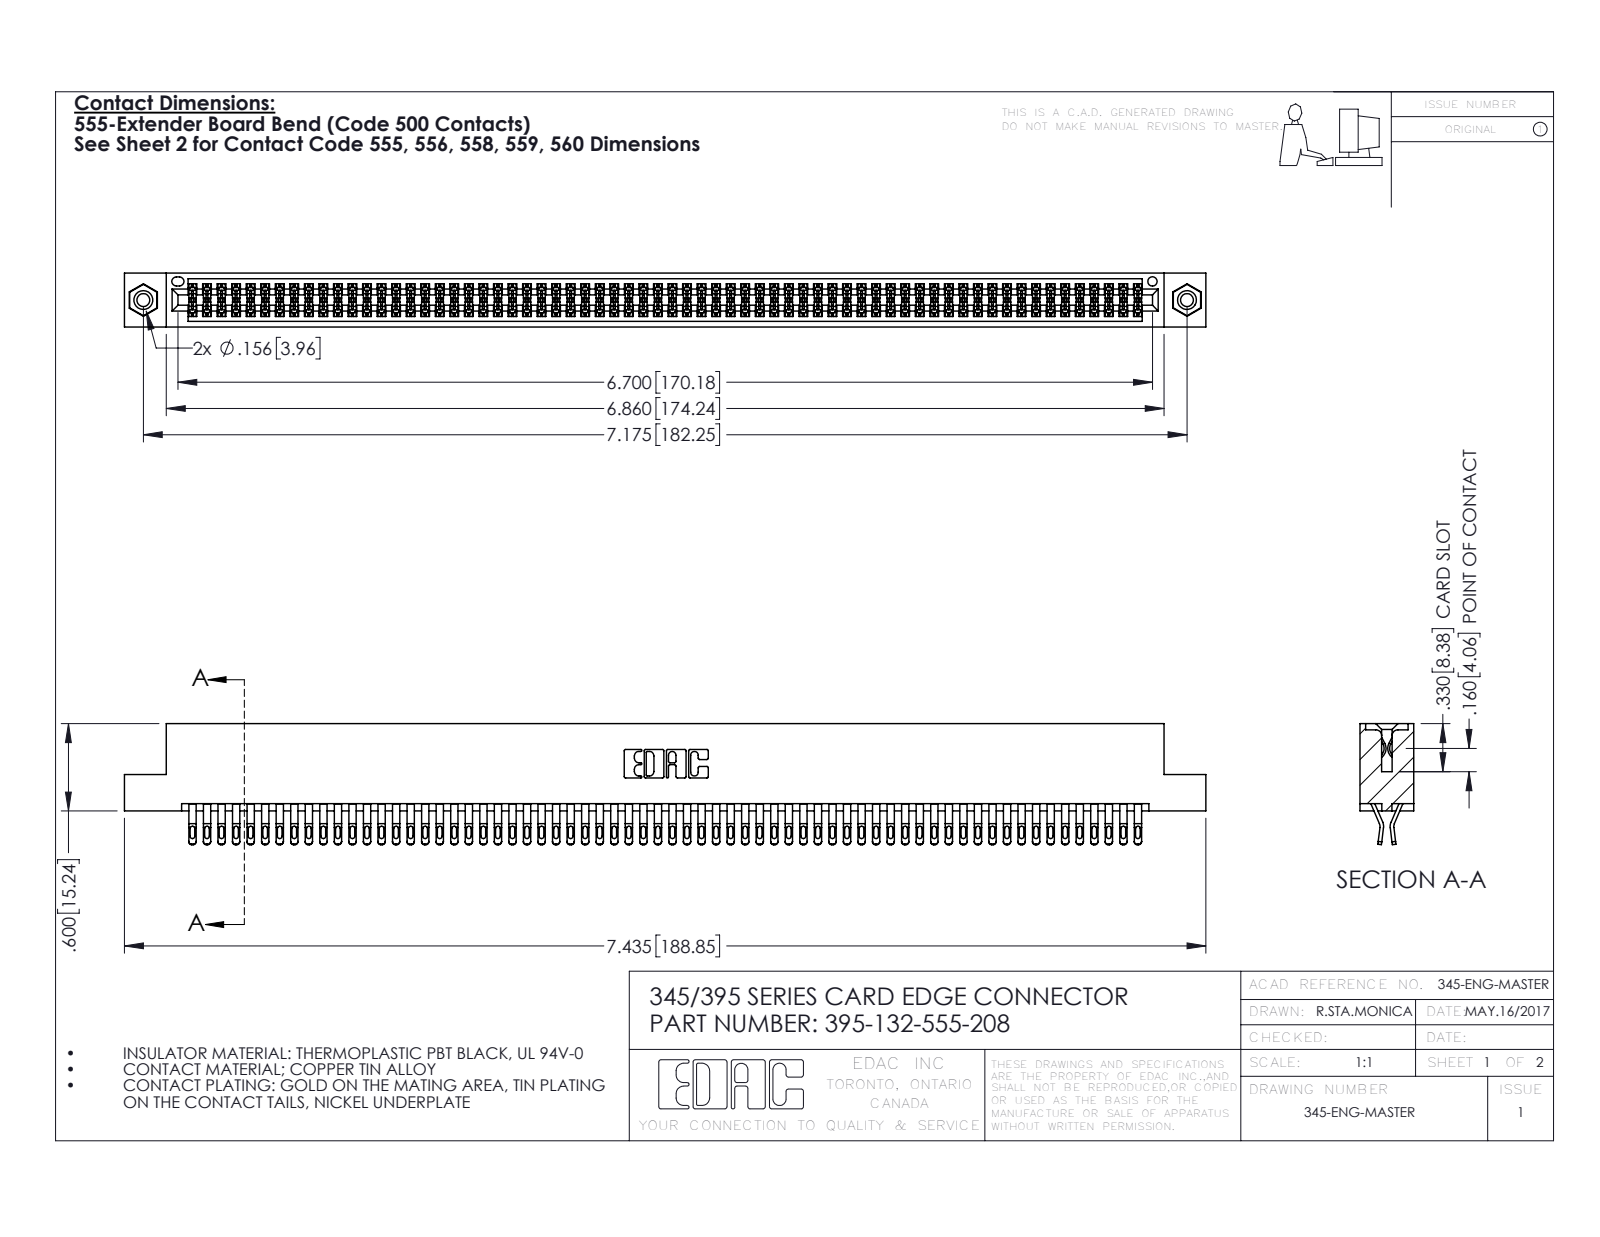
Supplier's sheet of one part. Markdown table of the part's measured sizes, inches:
| quantity | value |
| --- | --- |
| part name | 345-292-001_555 Tail; 395-132-555-208; 345 Part_Flush Mounting Lugs - 0.156 Dia-TI; 345-250-001_345-250-003-102 |
| STEP written by | SolidWorks 2016 (CONFIG_CONTROL_DESIGN) |
| units | inches |
| bodies | 135 solids, 7578 faces (4204 planar, 3358 cylindrical, 16 other) |
| overall size | 7.435 × 0.832 × 0.37 |
| volume | 1.156 in³ |
| surface area | 46.21 in² |
| round holes (diameter × count) | 0.089 × 2, 0.125 × 2, 0.156 × 2, 0.064 × 1 |
| round bosses / shafts (diameter × count) | 0.155 × 2 |
| partial cylindrical surfaces (radius × count) | 0.016 × 330, 0.02 × 264, 0.006 × 198, 0.01 × 22, 0.007 × 6, 0.031 × 6, 0.026 × 3, 0.01 × 2 |
| main face-to-face distances | 0.072, 0.298, 0.025, 0.37, 0.2, 0.098, 0.272, 0.225, 0.175, 0.149 |
| hole center spacings | 0.27, 6.939, 7.175 |
